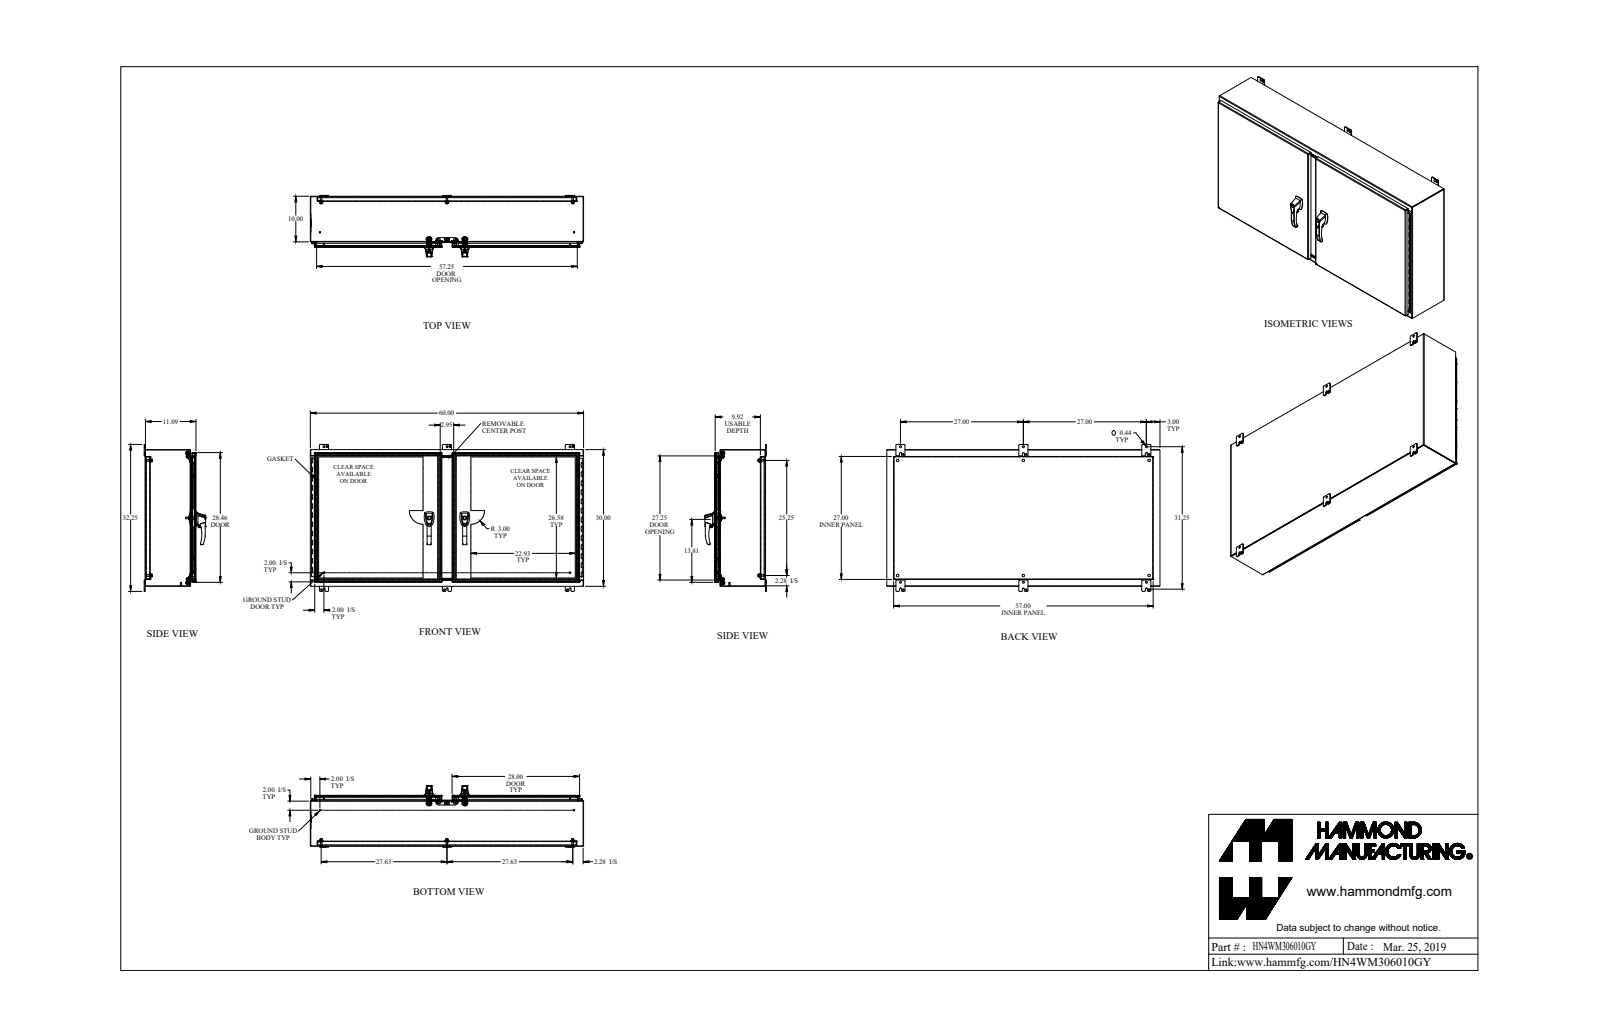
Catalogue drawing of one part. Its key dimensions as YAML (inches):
part_name: "HN4WM306010GY"
step_written_by: "SolidWorks 2018 (AUTOMOTIVE_DESIGN)"
units: inches
bodies: {solids: 101, faces: 2738, planar: 1311, cylindrical: 1159, other: 268}
overall_size: [60, 32.25, 13.487]
volume: 801.3
surface_area: 16609
round_holes:
  - {diameter: 0.304, count: 10}
  - {diameter: 0.313, count: 6}
  - {diameter: 0.563, count: 6}
  - {diameter: 0.25, count: 5}
  - {diameter: 0.307, count: 5}
  - {diameter: 0.281, count: 4}
  - {diameter: 0.313, count: 4}
  - {diameter: 0.39, count: 4}
  - {diameter: 0.445, count: 4}
  - {diameter: 0.201, count: 3}
  - {diameter: 0.437, count: 3}
  - {diameter: 0.11, count: 2}
round_bosses_or_shafts:
  - {diameter: 0.281, count: 8}
  - {diameter: 1, count: 7}
  - {diameter: 0.65, count: 5}
  - {diameter: 0.375, count: 5}
  - {diameter: 0.33, count: 5}
  - {diameter: 0.75, count: 4}
  - {diameter: 0.625, count: 4}
  - {diameter: 0.44, count: 4}
partial_cylinders:
  - {radius: 0.125, count: 33}
  - {radius: 0.018, count: 32}
  - {radius: 0.188, count: 26}
  - {radius: 0.25, count: 26}
  - {radius: 0.048, count: 21}
  - {radius: 0.143, count: 21}
  - {radius: 0.06, count: 20}
  - {radius: 0.5, count: 17}
face_to_face_distances: [0.095, 1.032, 11.09, 10.995, 0.095, 11.185, 11.09, 0.937, 1.127, 9.963]
hole_center_spacings: [27.625, 37.426, 6, 58.45, 26.869, 33.965, 60.746, 12]
